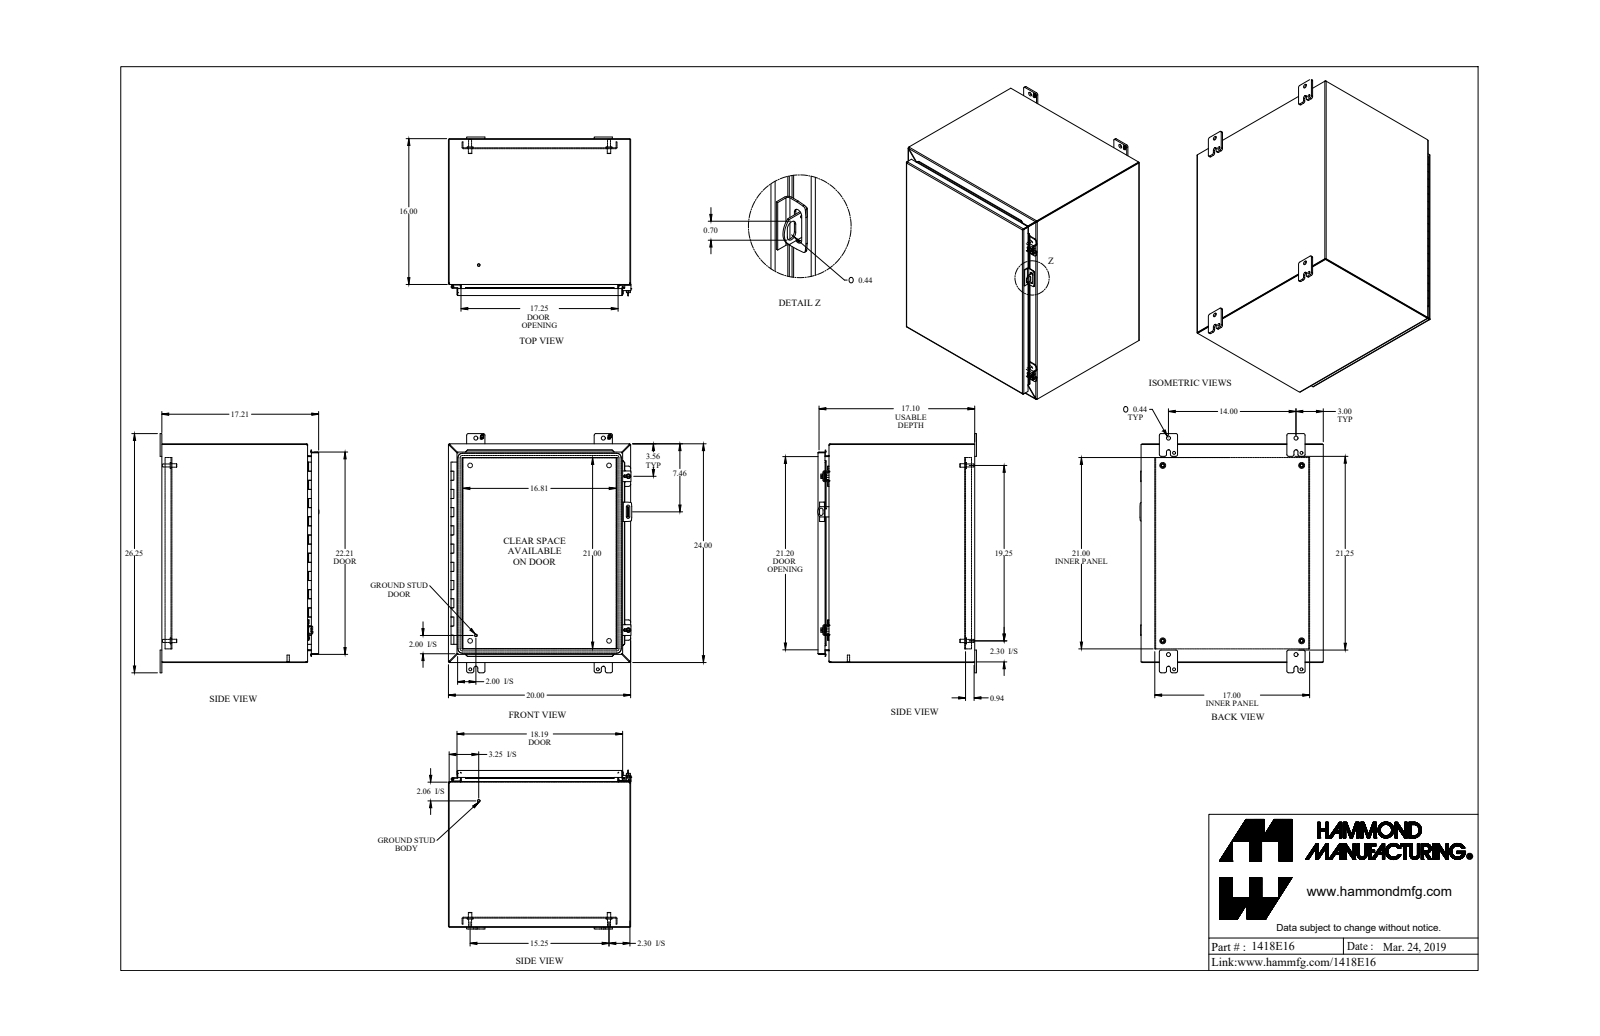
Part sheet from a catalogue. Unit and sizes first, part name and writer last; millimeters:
Units: millimetres
Overall size (bounding box): 666.8 × 511.2 × 442.9
Round holes (diameter × count): ⌀8 ×4, ⌀11.1 ×4, ⌀12.7 ×4, ⌀5.4 ×2, ⌀6.7 ×2, ⌀7.8 ×2, ⌀9.5 ×2, ⌀11.3 ×2, ⌀3.2 ×1, ⌀4.7 ×1
Round bosses / shafts (diameter × count): ⌀16.5 ×4, ⌀9.5 ×4, ⌀8.4 ×4, ⌀25.4 ×2, ⌀12.7 ×2, ⌀9.9 ×2, ⌀7.1 ×2, ⌀6.4 ×2
Partial cylindrical surfaces — rounded edges, fillets, slot ends (radius × count): R4.8 ×26, R0.9 ×18, R2.7 ×18, R1.2 ×13, R3.6 ×13, R6.4 ×12, R0.2 ×8, R1 ×8
Main face-to-face distances: 1.8, 434.7, 506.2, 607.8, 432.8, 436.5, 23.8, 2.4, 25.6, 504.3
Hole centre spacings: 355.6, 41.3, 44.1, 387.4, 442.3, 489, 603.3, 623.8
Volume: 3 926 000 mm³ · Surface area: 4 074 000 mm²
Bodies: 40 solids, 1006 faces (677 planar, 267 cylindrical, 62 other)
Part name (STEP PRODUCT): 1418E16
STEP written by: SolidWorks 2019 (AUTOMOTIVE_DESIGN)
